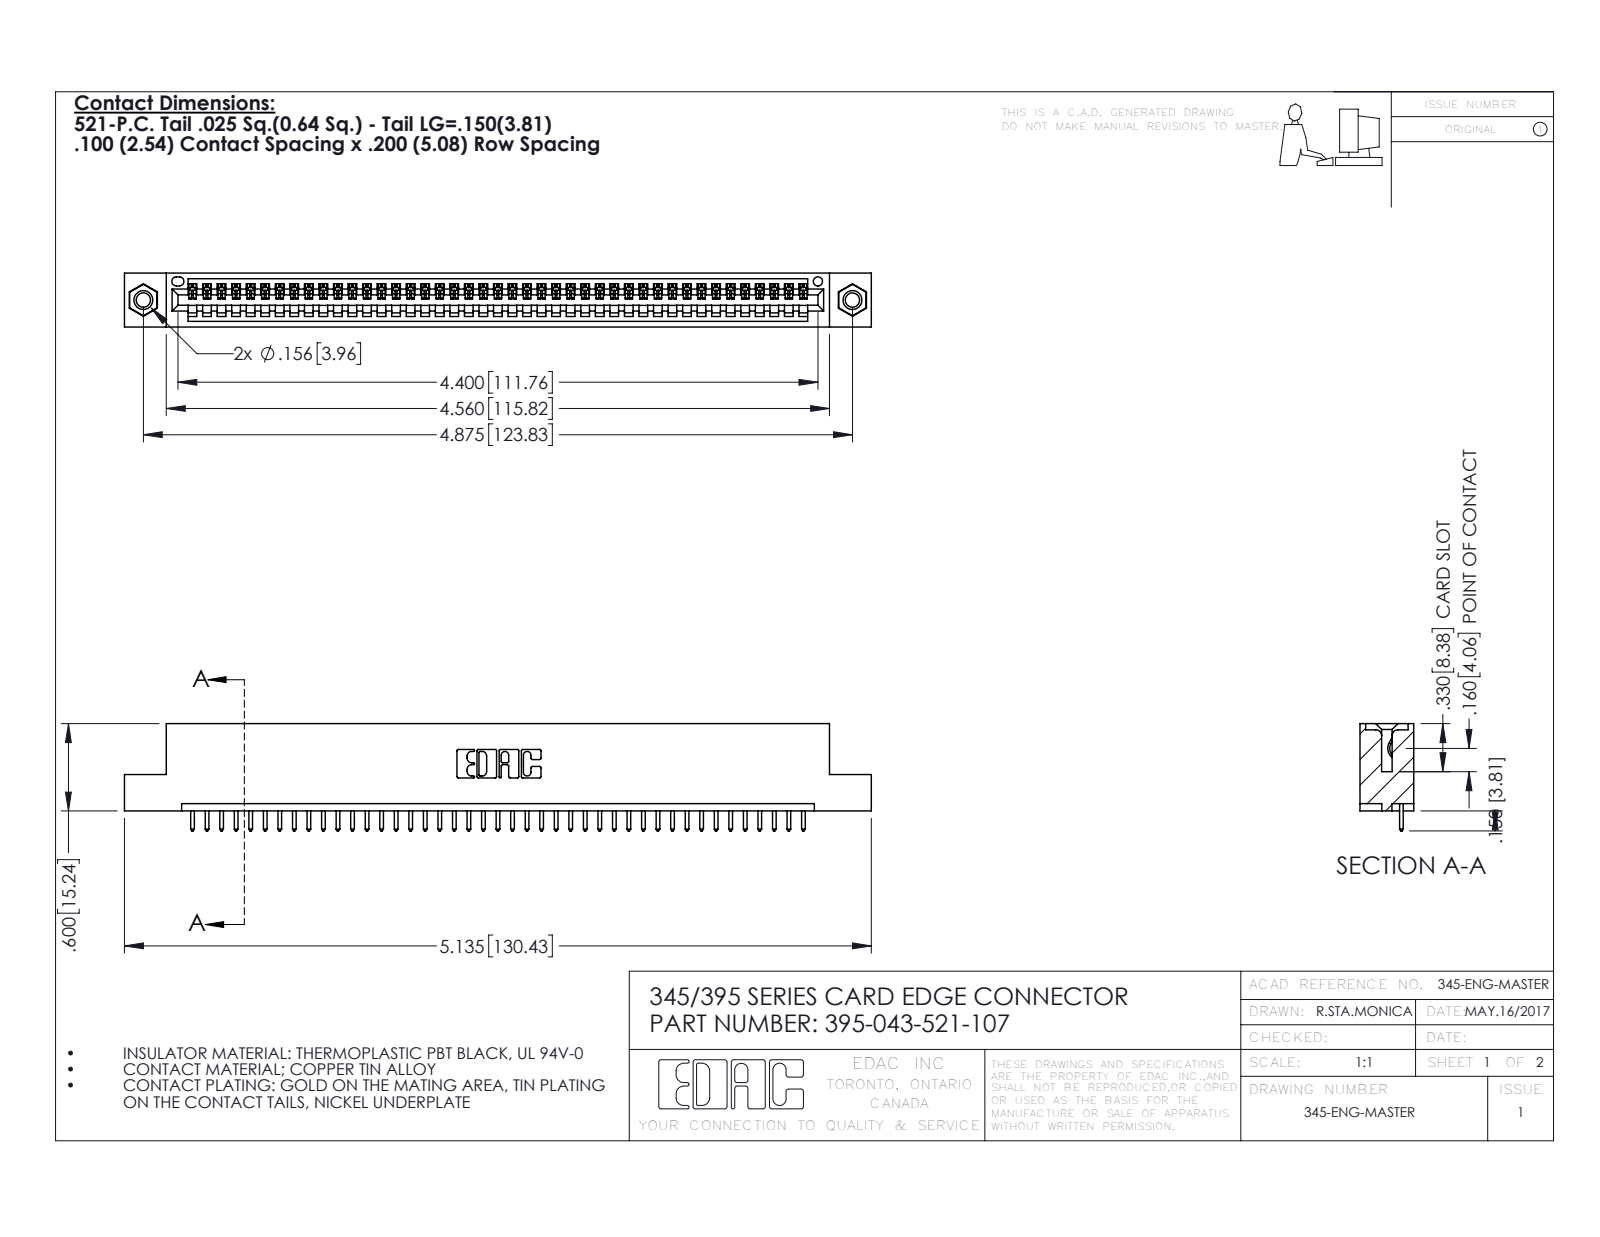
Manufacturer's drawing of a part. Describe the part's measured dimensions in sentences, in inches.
The part is named "345 Part_Flush Mounting Lugs - 0.156 Dia-TI; 345-292-001_345-293-121; 395-043-521-107; 345-250-001_345-250-005-103". Its 3-D file was written by "SolidWorks 2016 (CONFIG_CONTROL_DESIGN)". It is 46 solids with 2680 faces: 1832 planar, 832 cylindrical and 16 other. Overall it measures 5.135 by 0.737 by 0.37 inches. Its volume is 0.748 cubic inches and its surface area 24.58 square inches. Round holes: 2 of diameter 0.098, 2 of diameter 0.125, 2 of diameter 0.156, 1 of diameter 0.064. Round bosses or shafts: 2 of diameter 0.155. Partial cylindrical surfaces (rounded edges, fillets, slot ends): 86 of radius 0.006, 86 of radius 0.01, 22 of radius 0.01, 6 of radius 0.007, 6 of radius 0.031, 3 of radius 0.026, 2 of radius 0.031, 2 of radius 0.04. The main face-to-face distances are 0.072, 0.298, 0.37, 0.2, 0.098, 0.272, 0.025, 0.225, 0.149, 0.072. The hole center spacings are 0.27, 4.639, 4.875.
